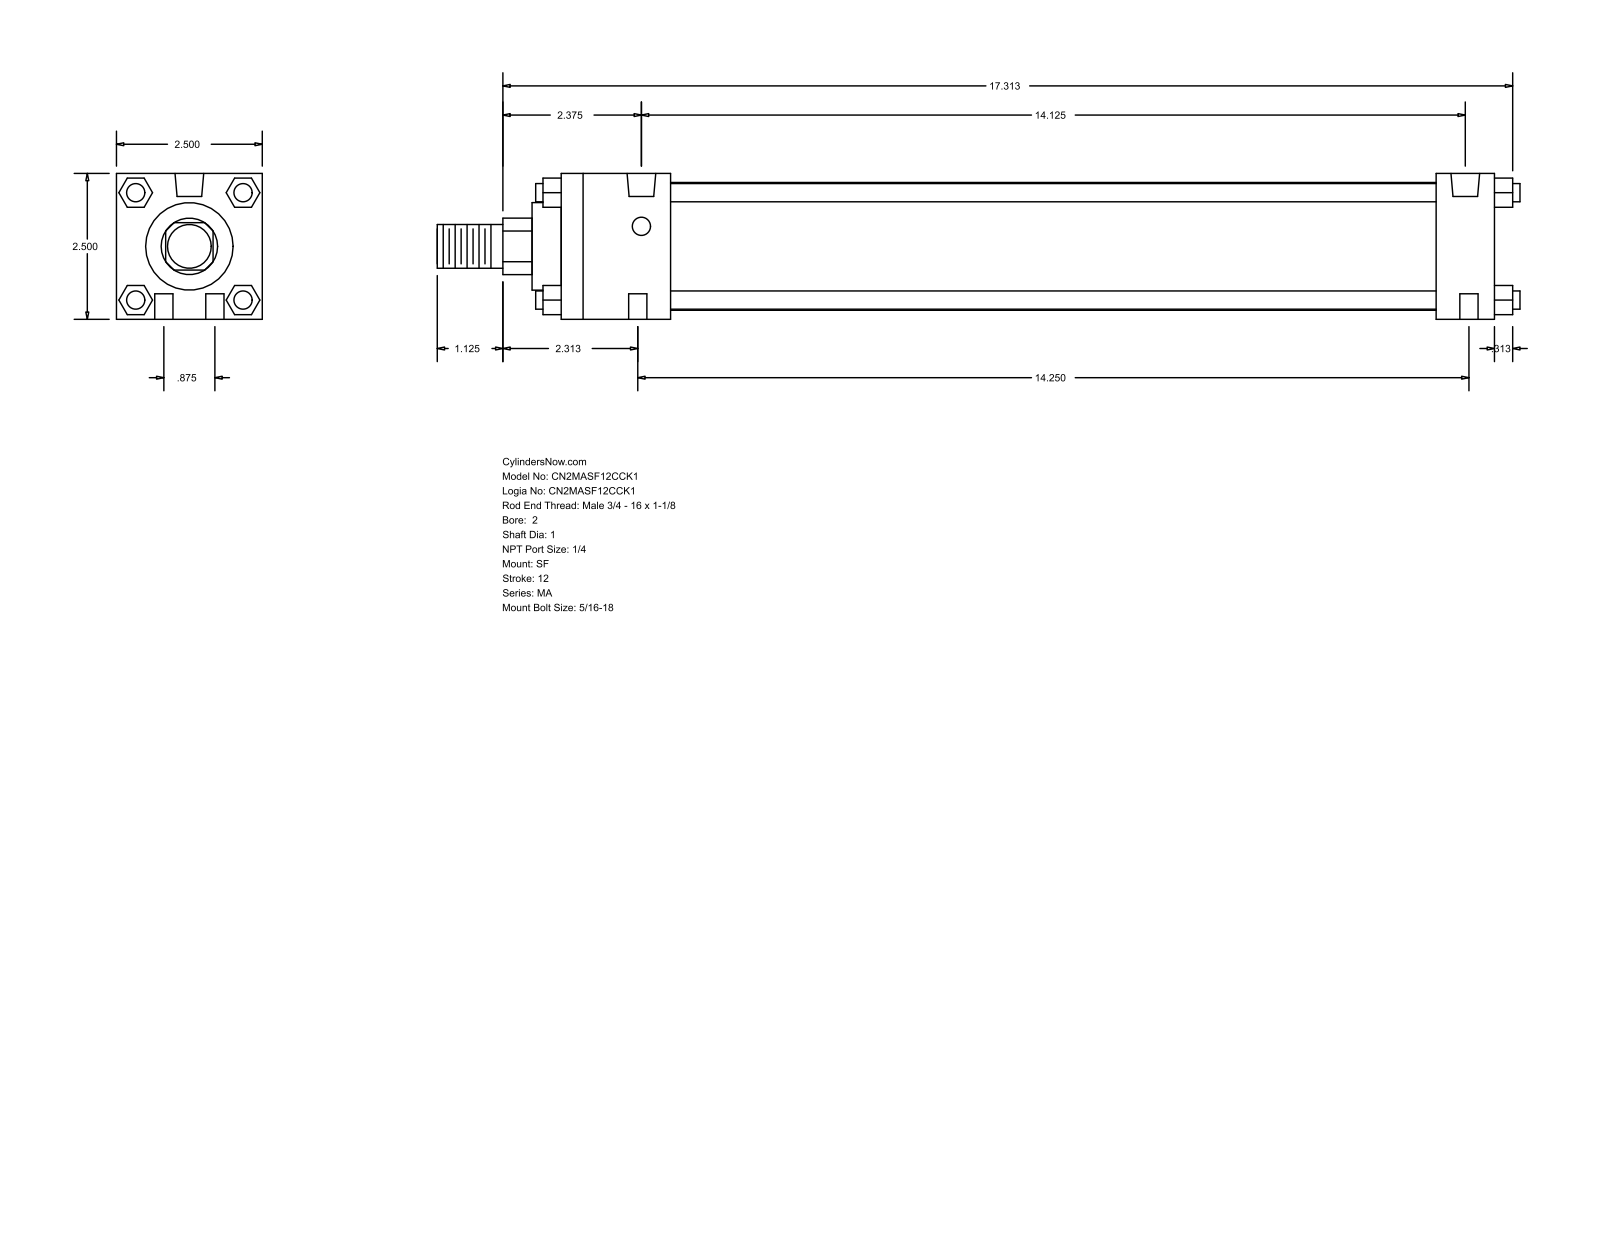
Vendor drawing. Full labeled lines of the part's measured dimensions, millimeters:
Part name (STEP PRODUCT): MA_SF__0200_1
STEP written by: GSSL Pune (CONFIG_CONTROL_DESIGN)
Units: millimetres
Bodies: 0 solids, 124 faces (94 planar, 30 cylindrical, 0 other)
Overall size (bounding box): 471.49 × 63.5 × 63.5
Round holes (diameter × count): ⌀7.94 ×6, ⌀12.49 ×2
Round bosses / shafts (diameter × count): ⌀7.94 ×4, ⌀55.63 ×1, ⌀38.1 ×1, ⌀25.4 ×1, ⌀19.05 ×1
Partial cylindrical surfaces — rounded edges, fillets, slot ends (radius × count): R12.29 ×1
Main face-to-face distances: 63.5, 406.4, 12.7, 25.4, 381, 47.63, 333.37, 358.77, 40.47, 23.37
Hole centre spacings: 11.22, 360.53, 22.22, 358.77, 361.95, 362.63
